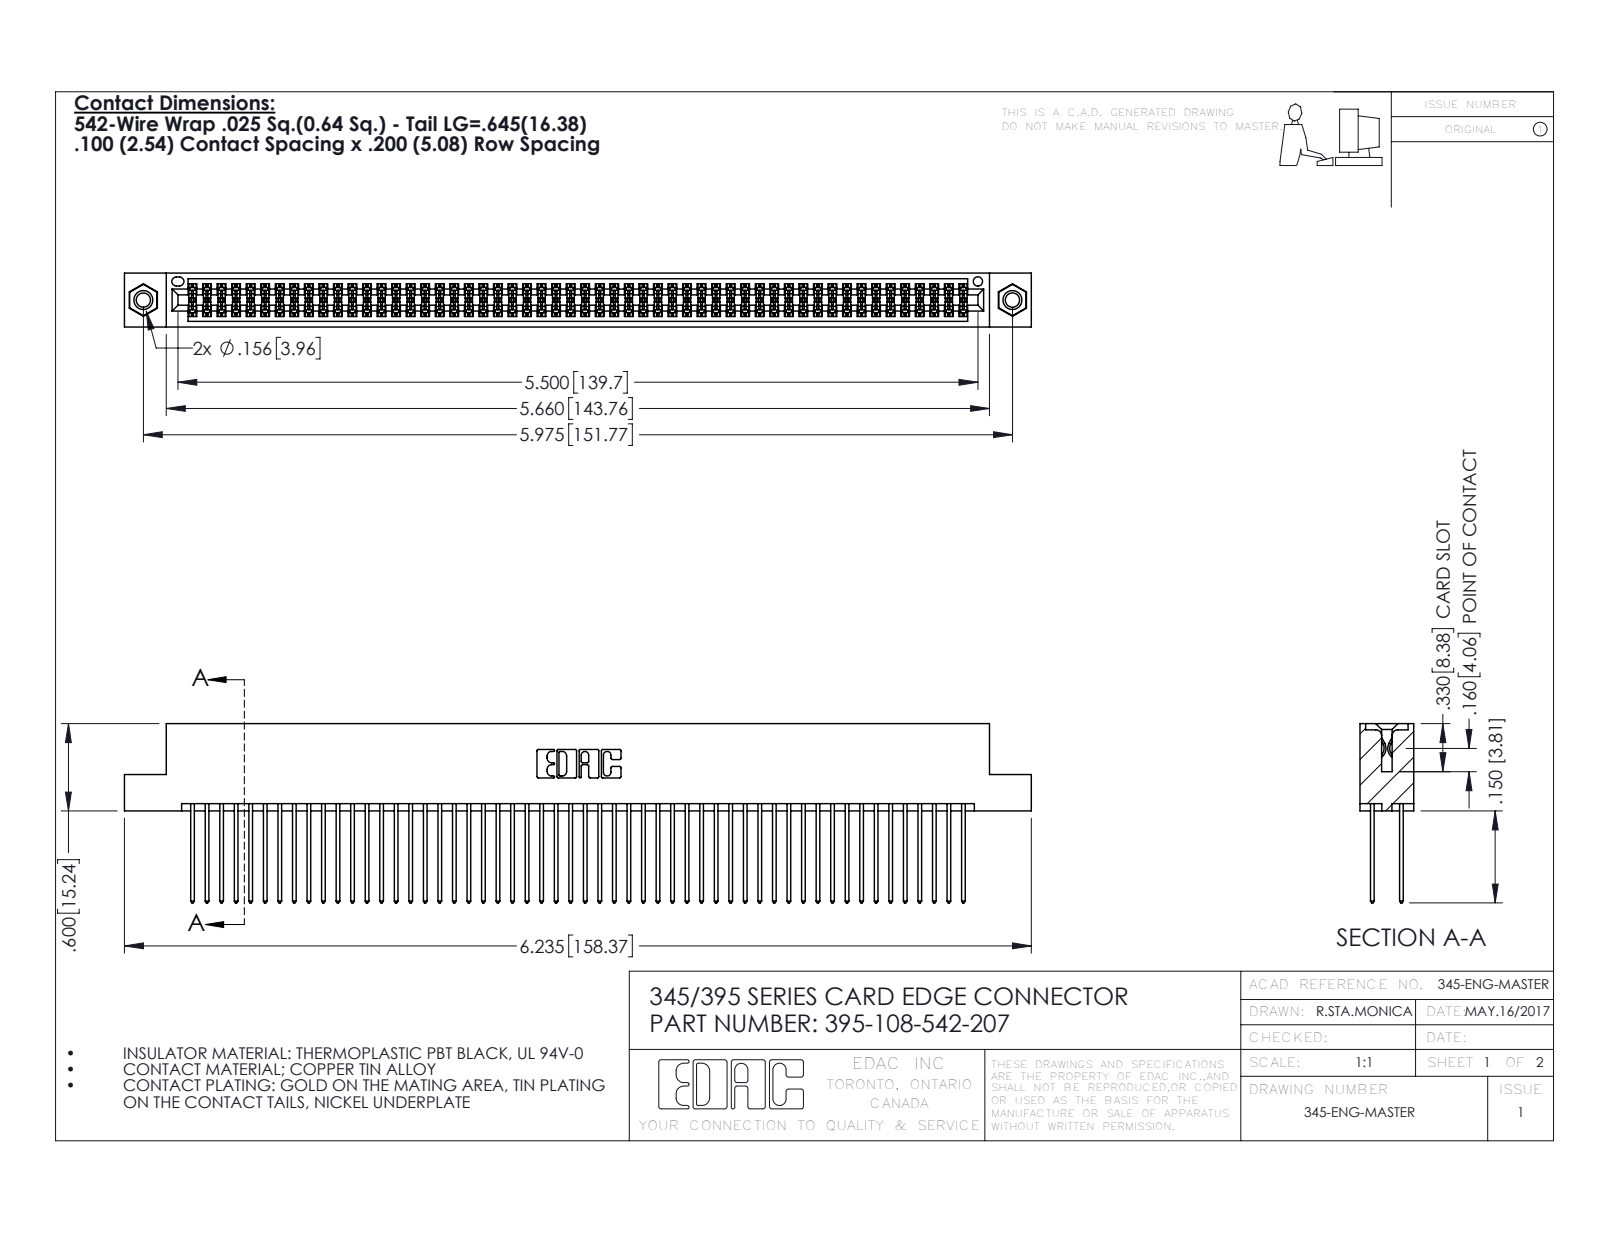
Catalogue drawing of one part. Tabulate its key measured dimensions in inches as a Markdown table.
| quantity | value |
| --- | --- |
| part name | 345-292-001_345-293-142; 345-250-001_345-250-005-103; 345 Part_Flush Mounting Lugs - 0.156 Dia-TI; 395-108-542-207 |
| STEP written by | SolidWorks 2016 (CONFIG_CONTROL_DESIGN) |
| units | inches |
| bodies | 111 solids, 5586 faces (3676 planar, 1894 cylindrical, 16 other) |
| overall size | 6.235 × 1.232 × 0.37 |
| volume | 0.975 in³ |
| surface area | 40.68 in² |
| round holes (diameter × count) | 0.098 × 2, 0.125 × 2, 0.156 × 2, 0.064 × 1 |
| round bosses / shafts (diameter × count) | 0.155 × 2 |
| partial cylindrical surfaces (radius × count) | 0.006 × 162, 0.01 × 108, 0.01 × 22, 0.007 × 6, 0.031 × 6, 0.026 × 3, 0.014 × 2, 0.019 × 2 |
| main face-to-face distances | 0.072, 0.298, 0.2, 0.098, 0.272, 0.025, 0.225, 0.37, 0.175, 0.149 |
| hole center spacings | 0.27, 5.739, 5.975 |
